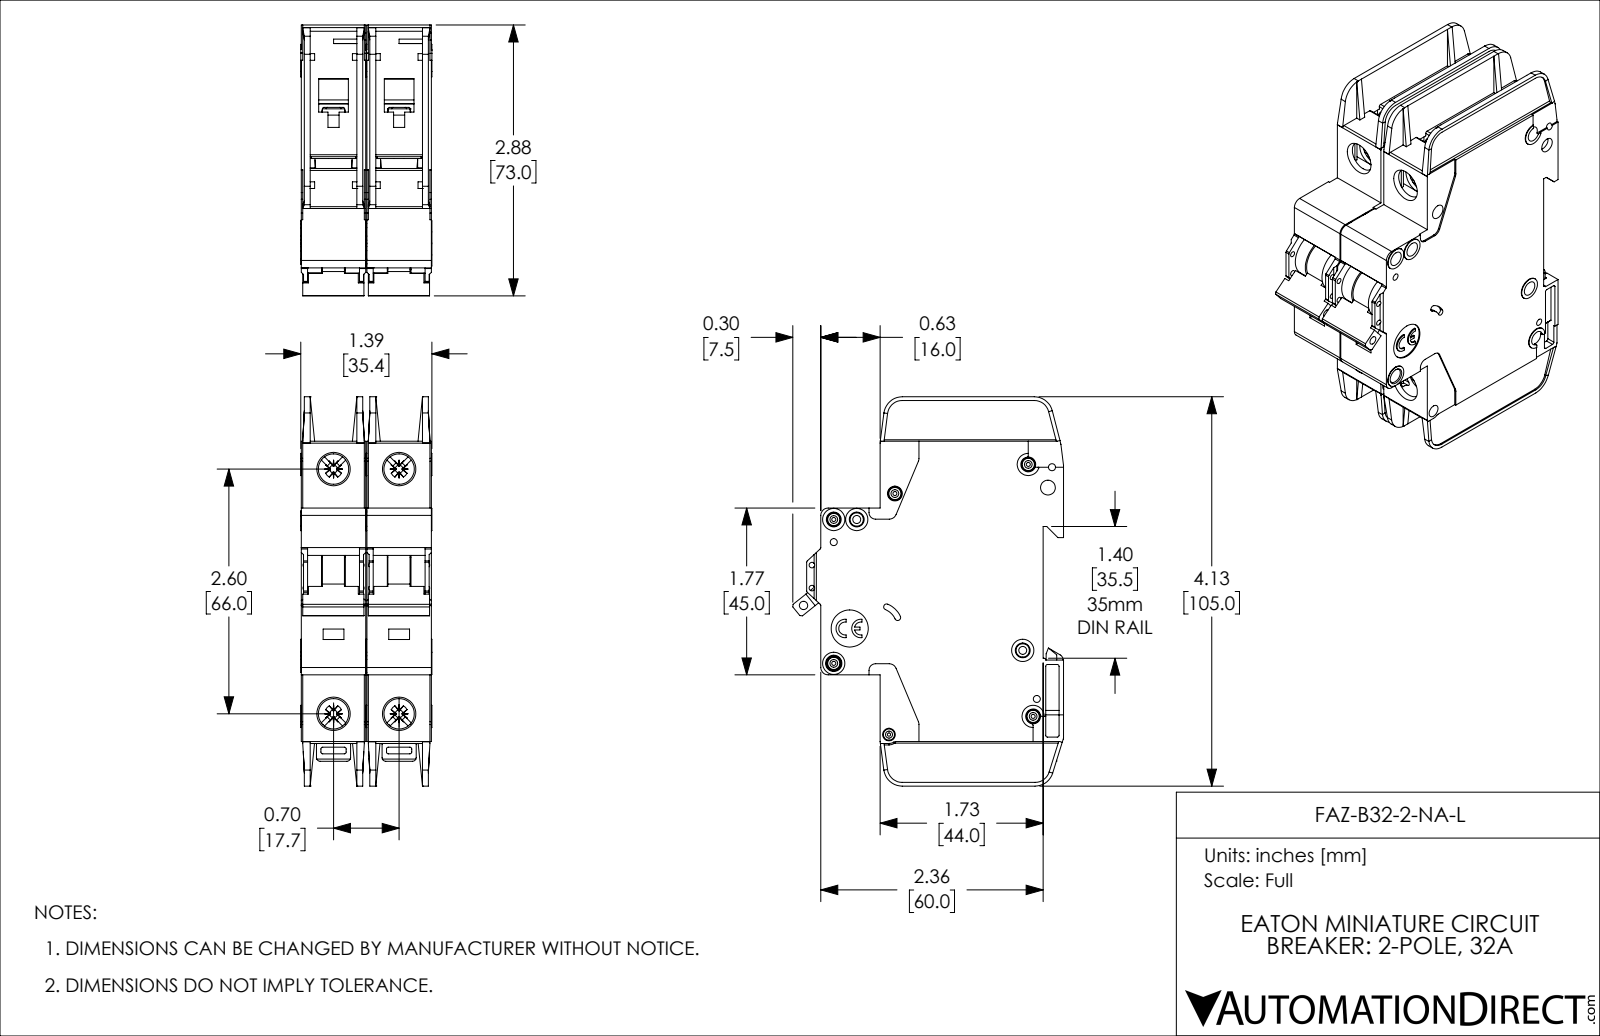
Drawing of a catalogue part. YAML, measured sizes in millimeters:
part_name: "FAZ-B32-2-NA-L"
step_written_by: "SolidWorks 2019 (AUTOMOTIVE_DESIGN)"
units: millimeters
bodies: {solids: 2, faces: 2254, planar: 1342, cylindrical: 714, other: 198}
overall_size: [105, 73.1, 35.4]
volume: 153500
surface_area: 52910
round_holes:
  - {diameter: 4, count: 8}
  - {diameter: 1.1, count: 5}
  - {diameter: 1.9, count: 4}
  - {diameter: 8.2, count: 4}
  - {diameter: 1.5, count: 2}
  - {diameter: 2.2, count: 2}
  - {diameter: 0.9, count: 1}
  - {diameter: 2.3, count: 1}
  - {diameter: 2.5, count: 1}
  - {diameter: 3.4, count: 1}
  - {diameter: 10, count: 1}
round_bosses_or_shafts:
  - {diameter: 3.3, count: 5}
  - {diameter: 6, count: 4}
  - {diameter: 3, count: 3}
  - {diameter: 2.5, count: 2}
partial_cylinders:
  - {radius: 0.5, count: 57}
  - {radius: 0.4, count: 20}
  - {radius: 1, count: 14}
  - {radius: 2, count: 10}
  - {radius: 1.1, count: 8}
  - {radius: 0.2, count: 5}
  - {radius: 5, count: 5}
  - {radius: 0.3, count: 4}
face_to_face_distances: [17.7, 1.2, 17.4, 15, 2.4, 16.2, 13.8, 35.1, 18.9, 16.5]
hole_center_spacings: [6.2, 13.6, 17.7, 22.1, 66, 68.3, 4.8, 5.1]
